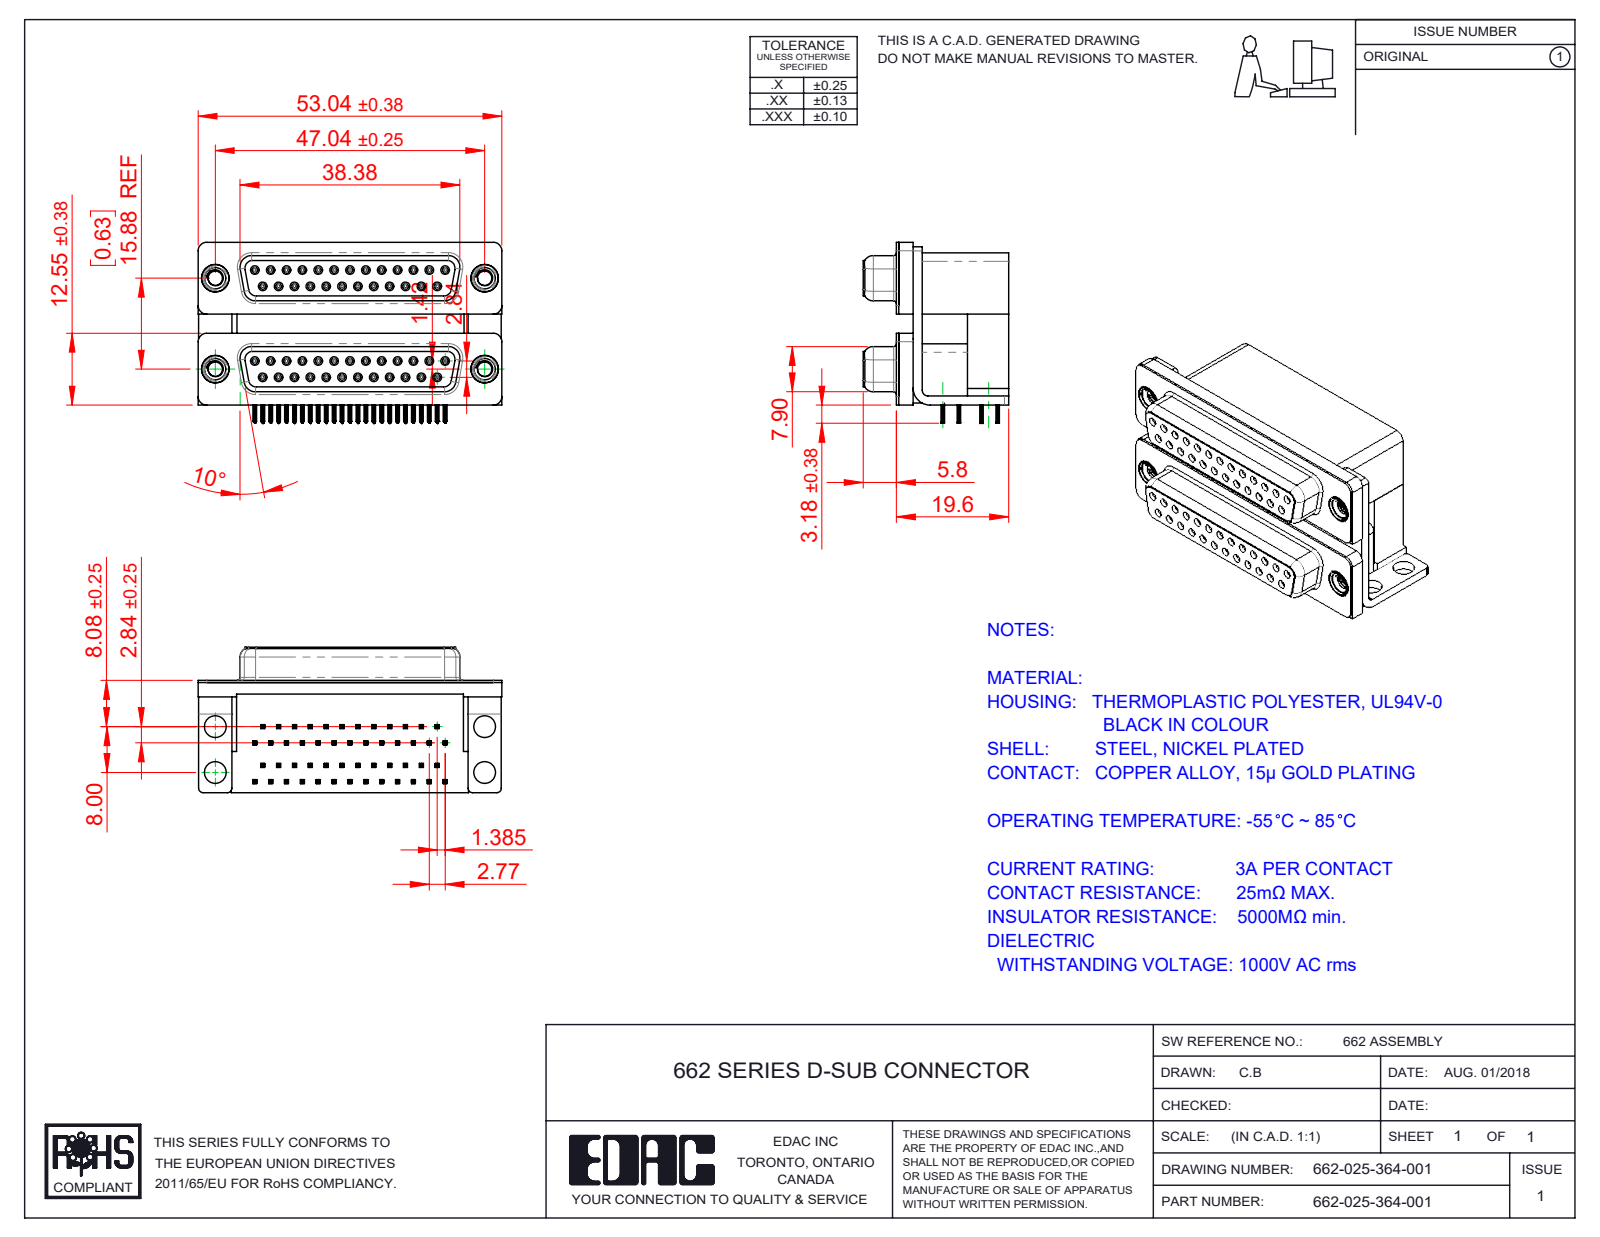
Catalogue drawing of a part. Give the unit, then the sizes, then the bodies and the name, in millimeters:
Units: millimetres
Overall size (bounding box): 53.04 × 31.61 × 25.4
Round holes (diameter × count): ⌀0.8 ×50, ⌀0.9 ×50, ⌀2.5 ×4, ⌀3.5 ×4, ⌀3.8 ×4, ⌀4 ×4, ⌀4.8 ×4, ⌀5 ×4
Round bosses / shafts (diameter × count): ⌀1.2 ×50, ⌀4.9 ×4, ⌀4.75 ×4, ⌀3.9 ×4
Partial cylindrical surfaces — rounded edges, fillets, slot ends (radius × count): R0.1 ×400, R0.15 ×200, R0.35 ×100, R0.34 ×50, R0.28 ×24, R1.35 ×18, R1.5 ×13, R0.5 ×8
Main face-to-face distances: 15.88, 19.2, 0.4, 7.2, 12, 10.7, 6.2, 16.7, 9.5, 2.5
Hole centre spacings: 3.16, 2.77, 5.54, 11.08, 8.31, 5.03, 13.85, 7.48
Volume: 22 866 mm³ · Surface area: 24 947 mm²
Bodies: 61 solids, 7796 faces (3576 planar, 1812 cylindrical, 2408 other)
Part name (STEP PRODUCT): 662 Shell_25 Contacts; 662 Mounting Bracket_NoneL; 662 Housing Upper_25 Contacts L; 662 Threaded Rivet_M3 (+7 more)
STEP written by: SolidWorks 2020 (CONFIG_CONTROL_DESIGN)
